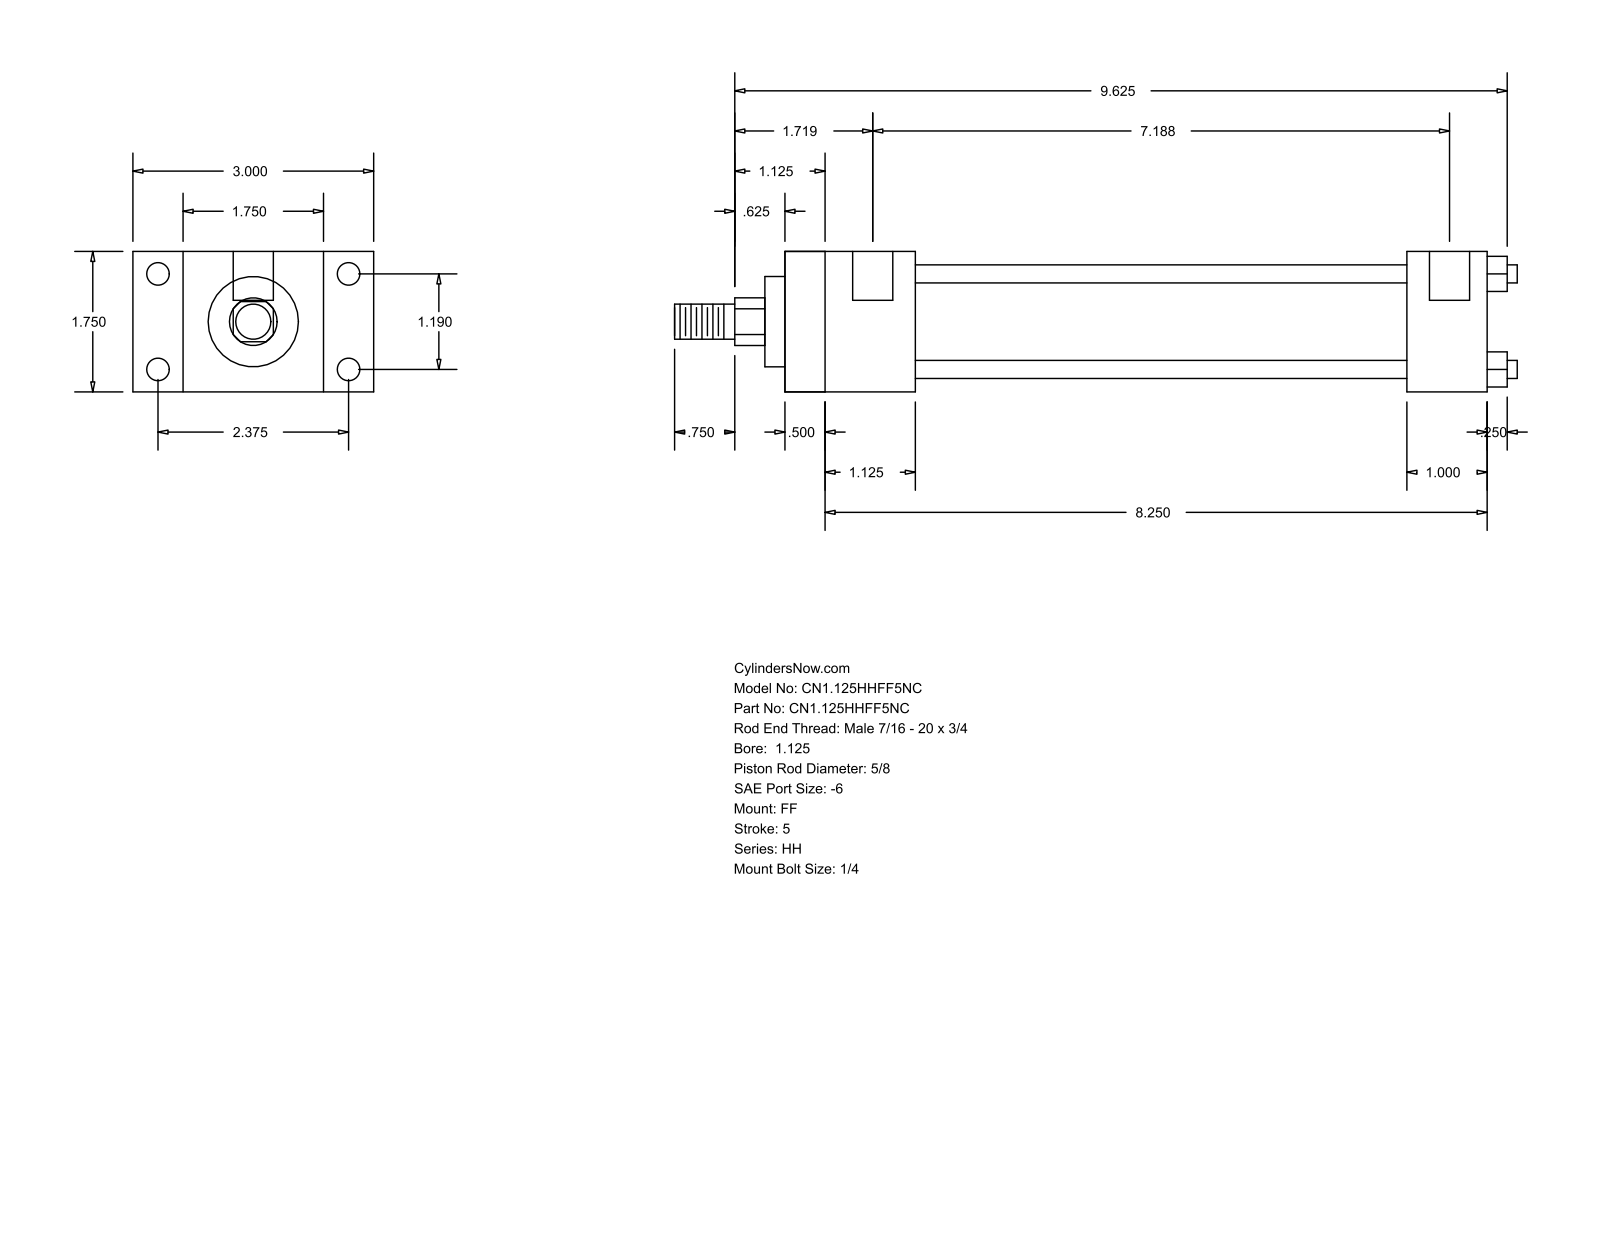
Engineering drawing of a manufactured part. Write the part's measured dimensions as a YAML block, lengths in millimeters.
part_name: "HH_FF__0112_0.625"
step_written_by: "GSSL Pune (CONFIG_CONTROL_DESIGN)"
units: millimeters
bodies: {solids: 0, faces: 92, planar: 64, cylindrical: 28, other: 0}
overall_size: [266.7, 76.2, 44.45]
round_holes:
  - {diameter: 5.56, count: 4}
  - {diameter: 7.14, count: 4}
  - {diameter: 12.7, count: 2}
round_bosses_or_shafts:
  - {diameter: 5.71, count: 4}
  - {diameter: 34.92, count: 1}
  - {diameter: 28.57, count: 1}
  - {diameter: 15.88, count: 1}
  - {diameter: 11.11, count: 1}
partial_cylinders:
  - {radius: 7.54, count: 1}
face_to_face_distances: [44.46, 222.24, 15.87, 12.69, 209.55, 28.58, 60.33, 25.4, 41.27, 196.84]
hole_center_spacings: [30.22, 60.32, 67.47, 179.39, 3.17, 182.56]
